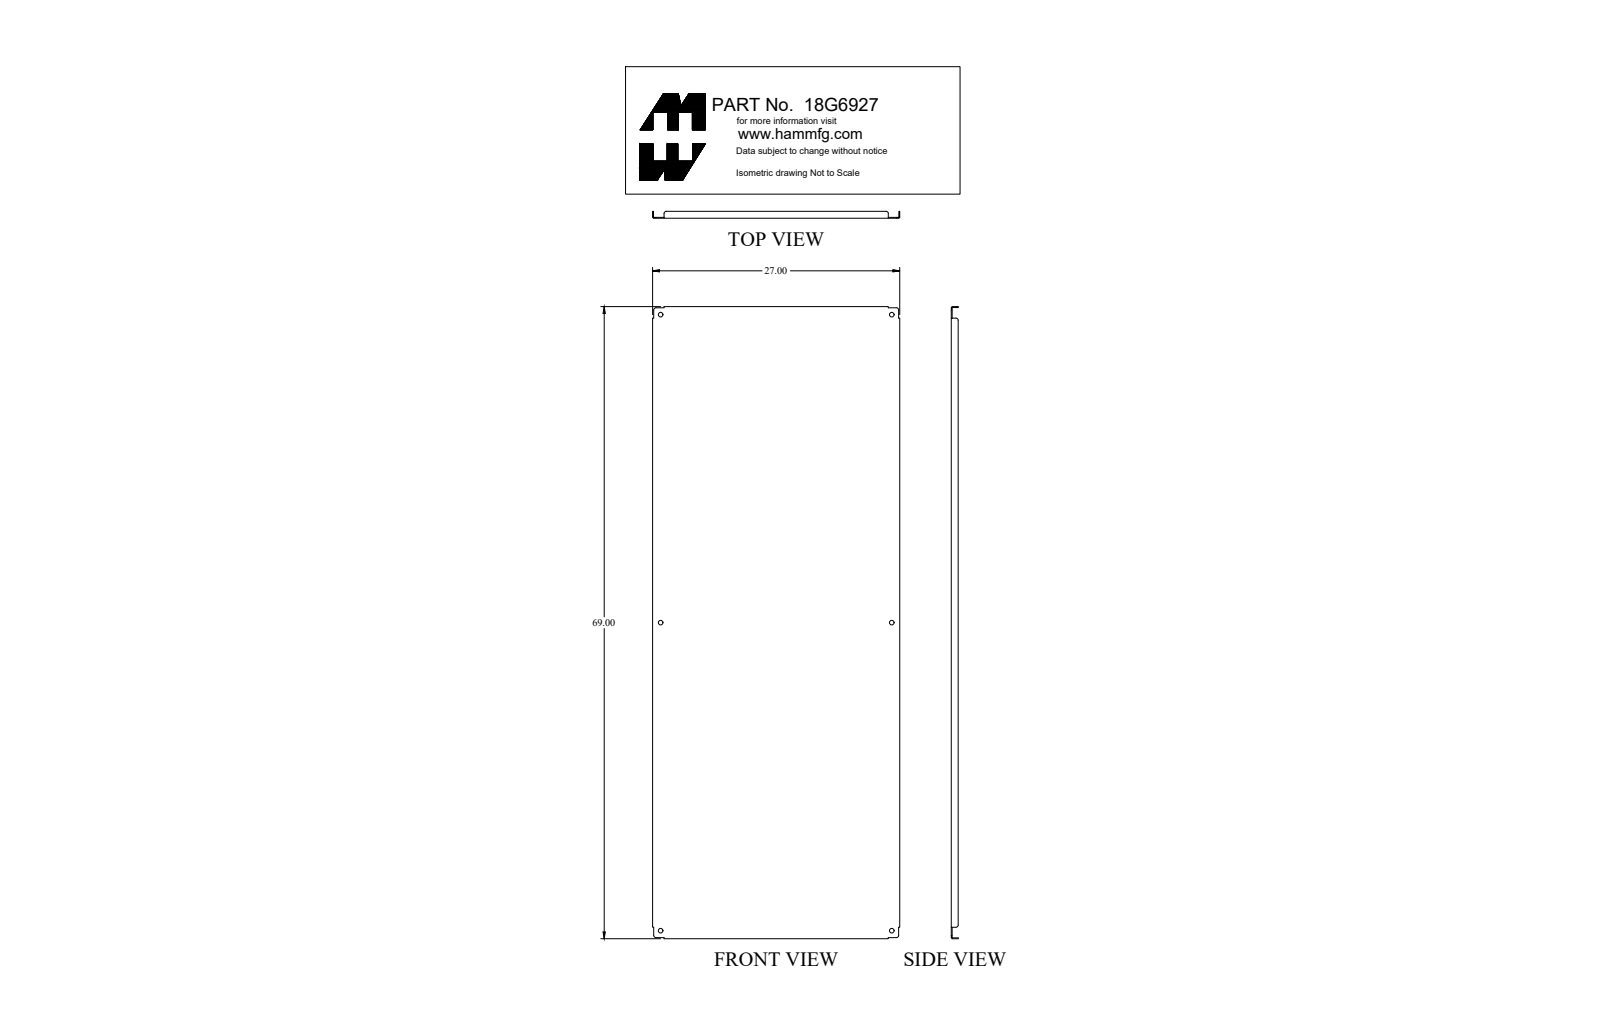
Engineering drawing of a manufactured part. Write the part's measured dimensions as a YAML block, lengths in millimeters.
part_name: "18G6927_Default"
step_written_by: "SolidWorks 2018 (CONFIG_CONTROL_DESIGN)"
units: millimeters
bodies: {solids: 1, faces: 62, planar: 30, cylindrical: 32, other: 0}
overall_size: [1752.6, 685.8, 19.1]
volume: 3073000
surface_area: 2559000
round_holes:
  - {diameter: 12.7, count: 6}
partial_cylinders:
  - {radius: 6.4, count: 8}
  - {radius: 0.8, count: 4}
  - {radius: 3.2, count: 4}
face_to_face_distances: [2.4, 683.4, 681, 685.8, 1750.2, 19.1, 16.6, 1752.6, 1747.8, 3.2]
hole_center_spacings: [854.1, 1068.1, 641.4, 1708.2, 1824.6]
